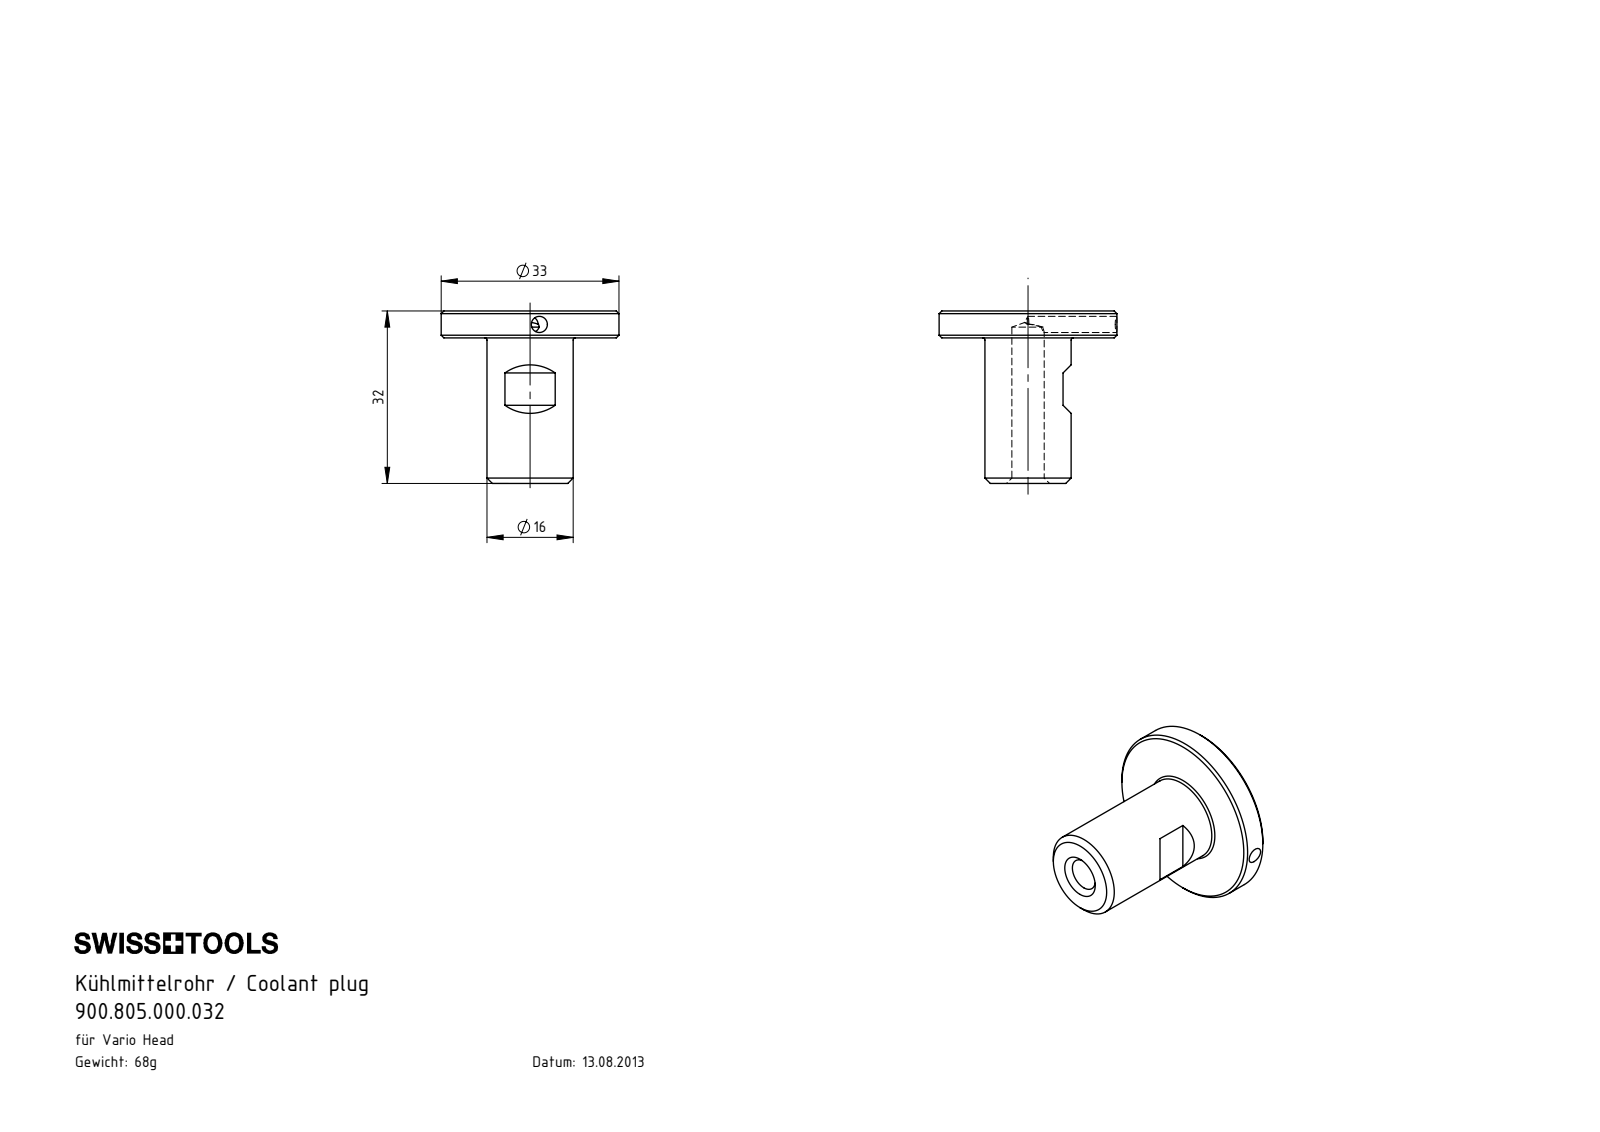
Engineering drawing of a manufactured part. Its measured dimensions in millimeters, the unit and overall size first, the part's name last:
Units: millimetres
Overall size (bounding box): 33 × 33 × 32
Round holes (diameter × count): ⌀3 ×1, ⌀6 ×1
Round bosses / shafts (diameter × count): ⌀33 ×1, ⌀16 ×1
Main face-to-face distances: 5, 27, 32
Volume: 8 641 mm³ · Surface area: 4 154 mm²
Bodies: 1 solid, 28 faces (6 planar, 8 cylindrical, 14 other)
Part name (STEP PRODUCT): 900.805.000.032
STEP written by: SolidWorks 2022 (CONFIG_CONTROL_DESIGN)
